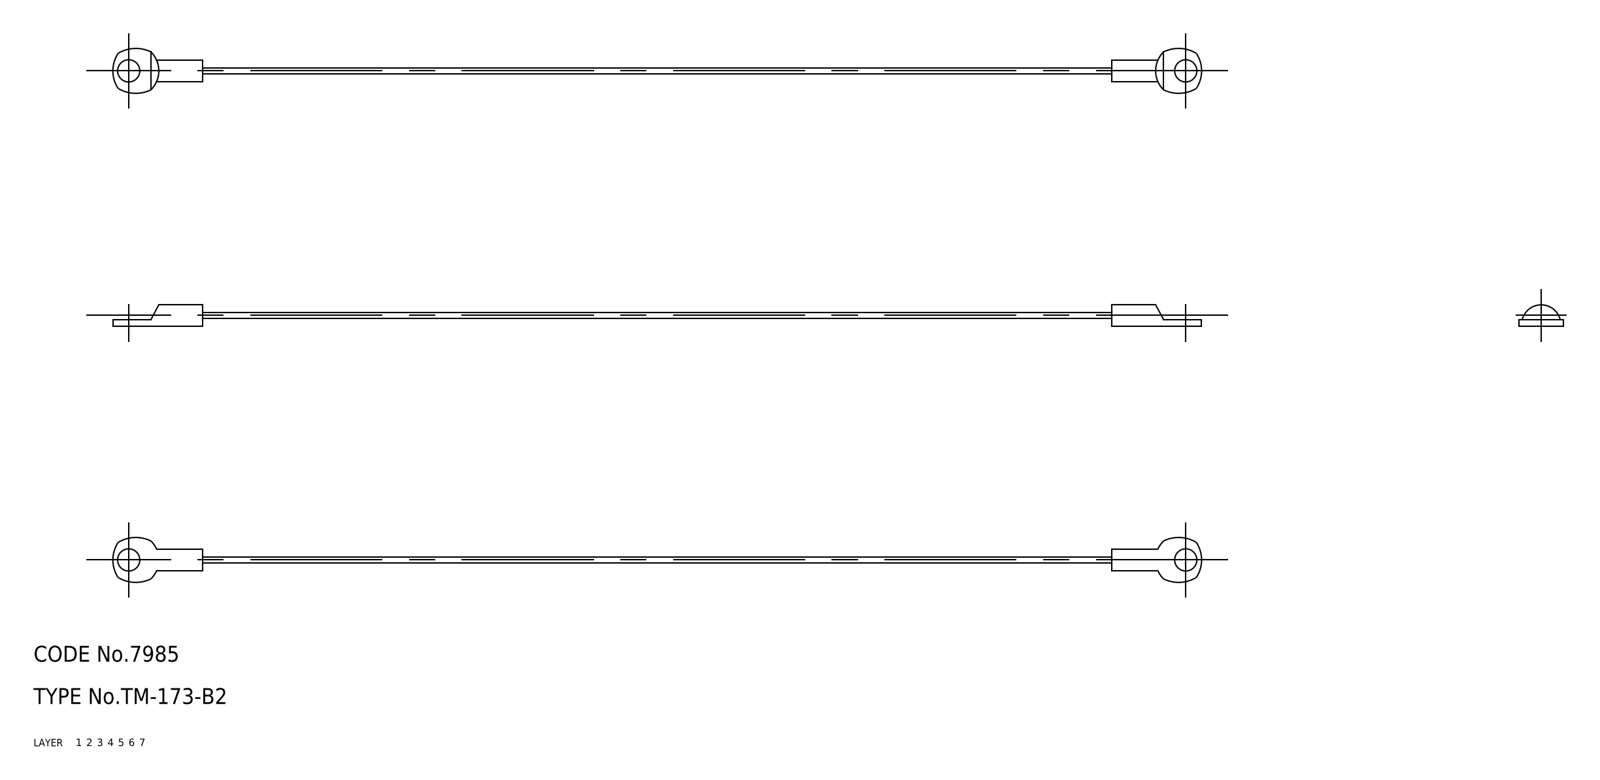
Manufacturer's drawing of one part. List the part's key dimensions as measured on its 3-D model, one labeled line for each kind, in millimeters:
Part name (STEP PRODUCT): terminal; wire; TM_173_B2_28381_36
STEP written by: CADfix (AUTOMOTIVE_DESIGN)
Units: millimetres
Bodies: 3 solids, 56 faces (0 planar, 0 cylindrical, 56 other)
Overall size (bounding box): 206 × 8.5 × 4
Volume: 524 mm³ · Surface area: 1 309 mm²
